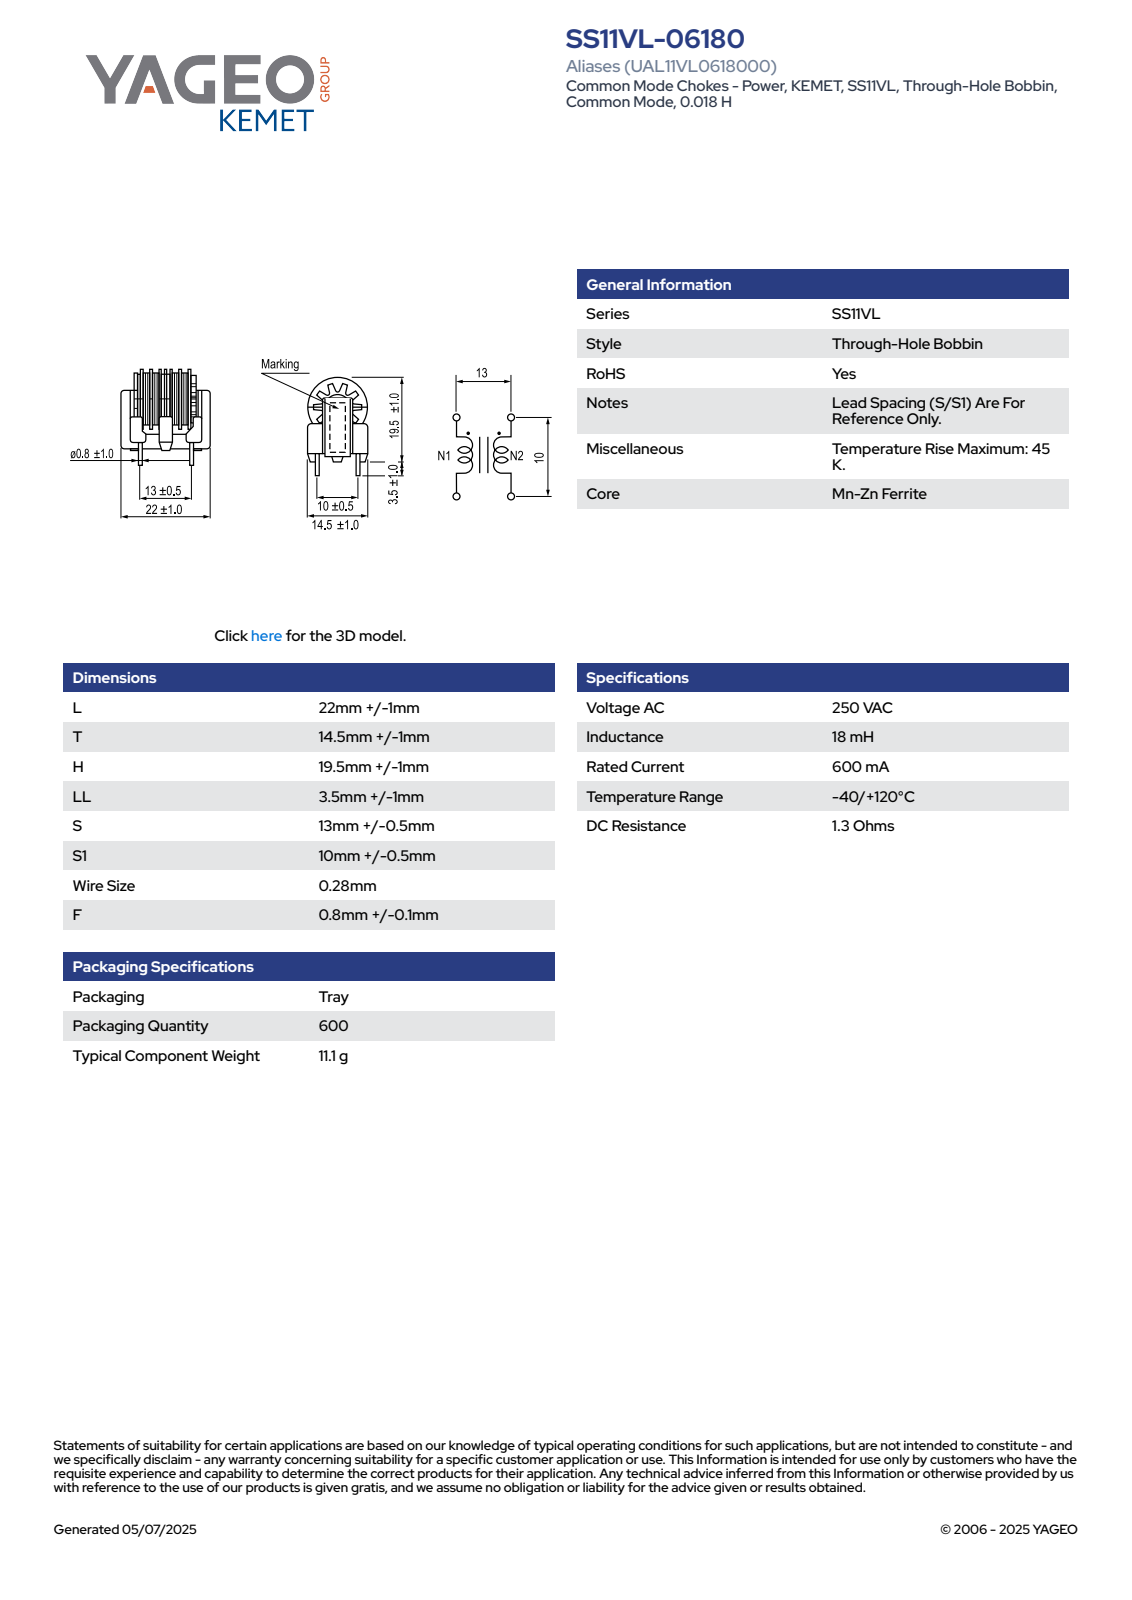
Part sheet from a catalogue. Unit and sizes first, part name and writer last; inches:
Units: inches
Overall size (bounding box): 0.945 × 0.906 × 0.61
Round holes (diameter × count): ⌀0.224 ×1, ⌀0.236 ×1
Round bosses / shafts (diameter × count): ⌀0.031 ×4, ⌀0.598 ×1, ⌀0.496 ×1, ⌀0.492 ×1
Partial cylindrical surfaces — rounded edges, fillets, slot ends (radius × count): R0.02 ×34, R0.039 ×22, R0.067 ×20, R0.008 ×8, R0.014 ×8, R0.016 ×8, R0.148 ×1, R0.236 ×1
Main face-to-face distances: 0.294, 0.067, 0.096, 0.096, 0.068, 0.028, 0.164, 0.097, 0.068, 0.069
Volume: 0.226 in³ · Surface area: 9.266 in²
Bodies: 1 solid, 626 faces (257 planar, 217 cylindrical, 152 other)
Part name (STEP PRODUCT): SS11VL(MAX-LOGO)
STEP written by: SolidWorks 2018 (AUTOMOTIVE_DESIGN)
